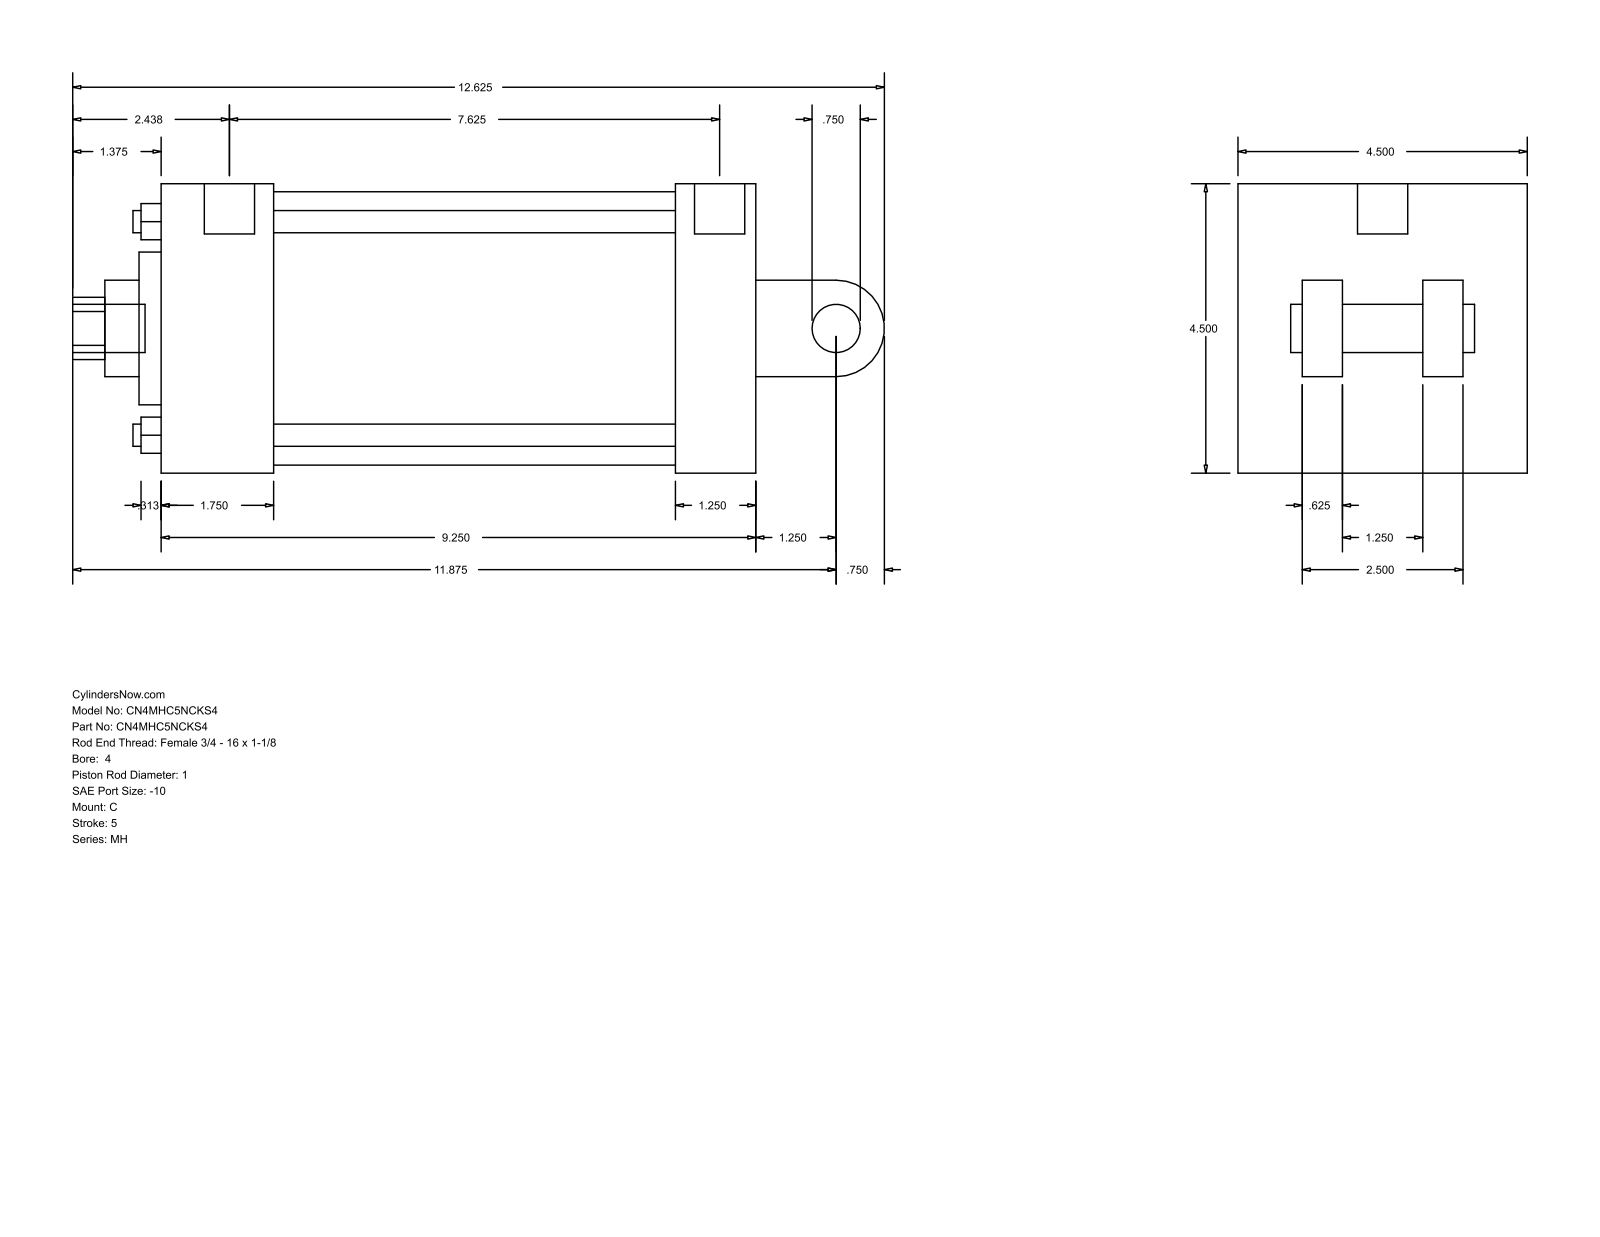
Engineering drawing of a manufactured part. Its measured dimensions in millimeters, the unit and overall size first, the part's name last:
Units: millimetres
Overall size (bounding box): 320.68 × 114.3 × 114.3
Round holes (diameter × count): ⌀8.76 ×4, ⌀8.73 ×2, ⌀19.84 ×1, ⌀25.4 ×1, ⌀38.1 ×1, ⌀60.33 ×1, ⌀107.95 ×1
Round bosses / shafts (diameter × count): ⌀19.05 ×2, ⌀8.73 ×2, ⌀19.84 ×1
Partial cylindrical surfaces — rounded edges, fillets, slot ends (radius × count): R12.29 ×1, R19.05 ×1
Main face-to-face distances: 114.3, 234.96, 31.76, 44.46, 203.2, 158.74, 190.5, 73.03, 15.87, 47.63
Hole centre spacings: 59.62, 84.32, 119.25, 1.59
Bodies: 0 solids, 101 faces (71 planar, 30 cylindrical, 0 other)
Part name (STEP PRODUCT): MH_C__0400_1
STEP written by: GSSL Pune (CONFIG_CONTROL_DESIGN)
